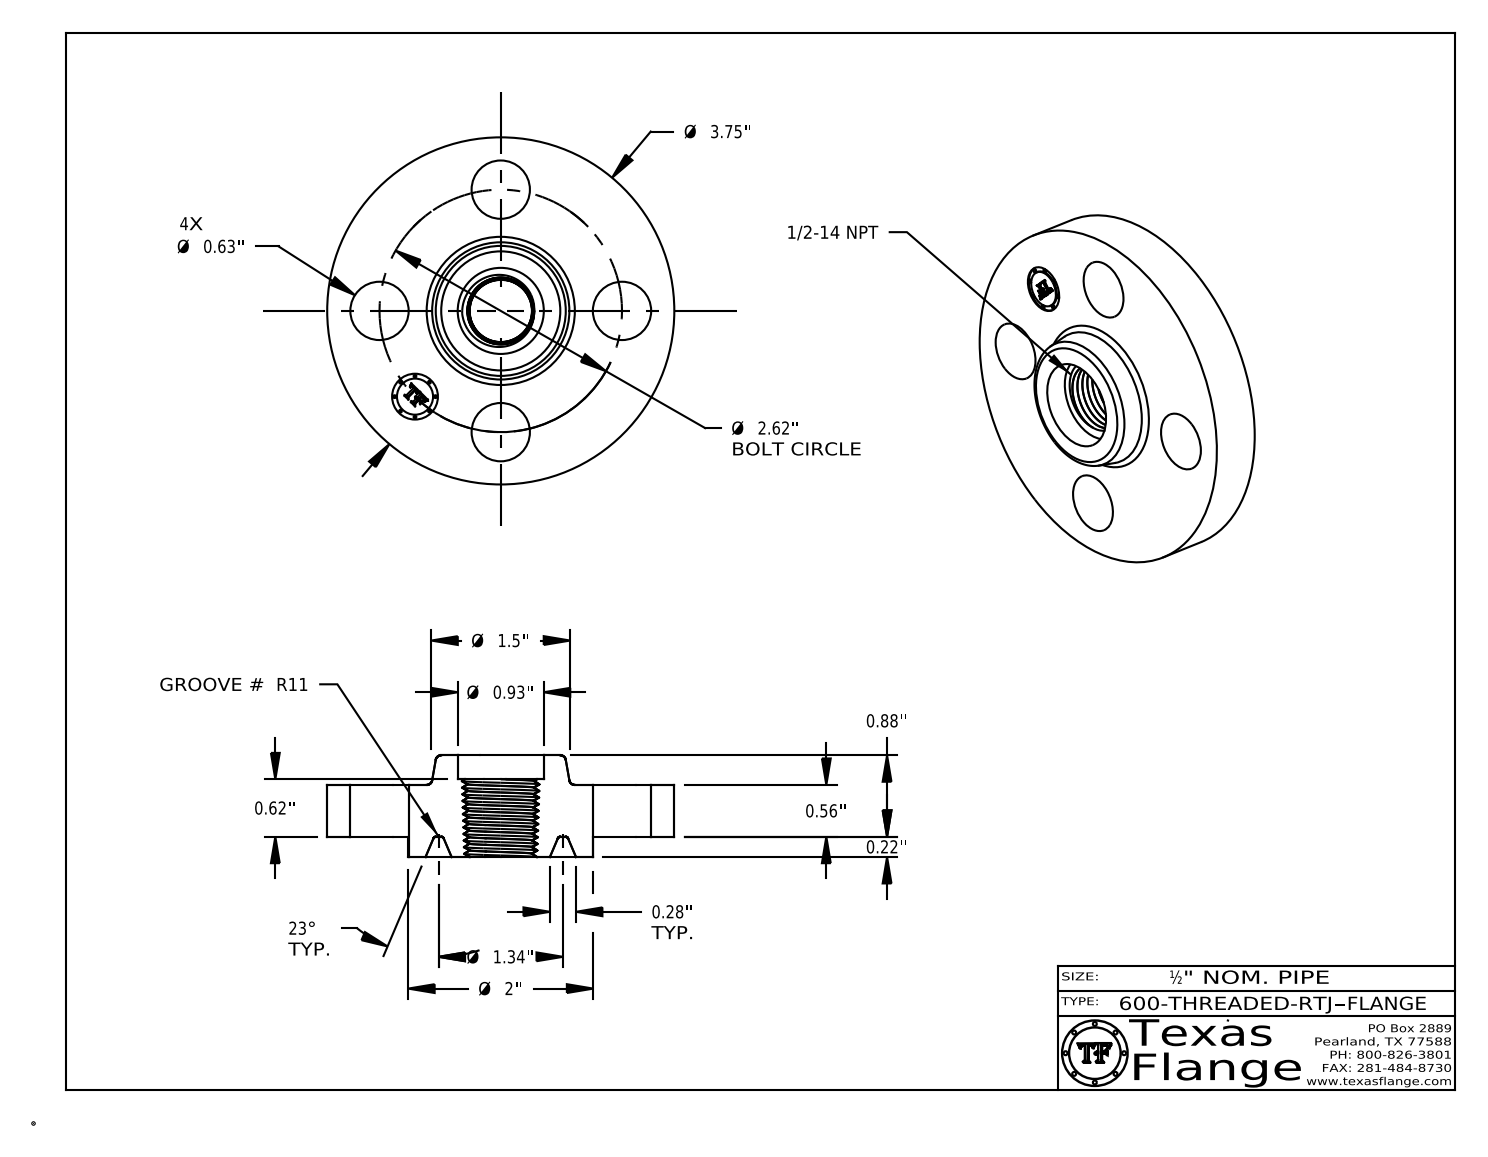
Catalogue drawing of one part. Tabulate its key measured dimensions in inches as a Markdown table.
| quantity | value |
| --- | --- |
| part name | 600-THREADED-RTJ |
| STEP written by | CATIA V5 STEP AP214 (AUTOMOTIVE_DESIGN) |
| units | inches |
| bodies | 1 solid, 547 faces (372 planar, 38 cylindrical, 137 other) |
| overall size | 3.75 × 3.75 × 1.099 |
| volume | 5.973 in³ |
| surface area | 37.91 in² |
| round holes (diameter × count) | 0.63 × 4, 0.495 × 1, 0.93 × 1 |
| round bosses / shafts (diameter × count) | 0.03 × 8, 3.75 × 1, 2 × 1, 0.39 × 1 |
| main face-to-face distances | 0.56, 0.219, 0.779, 1.099, 0.88, 0.32, 0.839, 0.62, 0.06, 0.26 |
| hole center spacings | 1.31, 1.852, 1.003, 2.42, 2.62, 1.31 |
